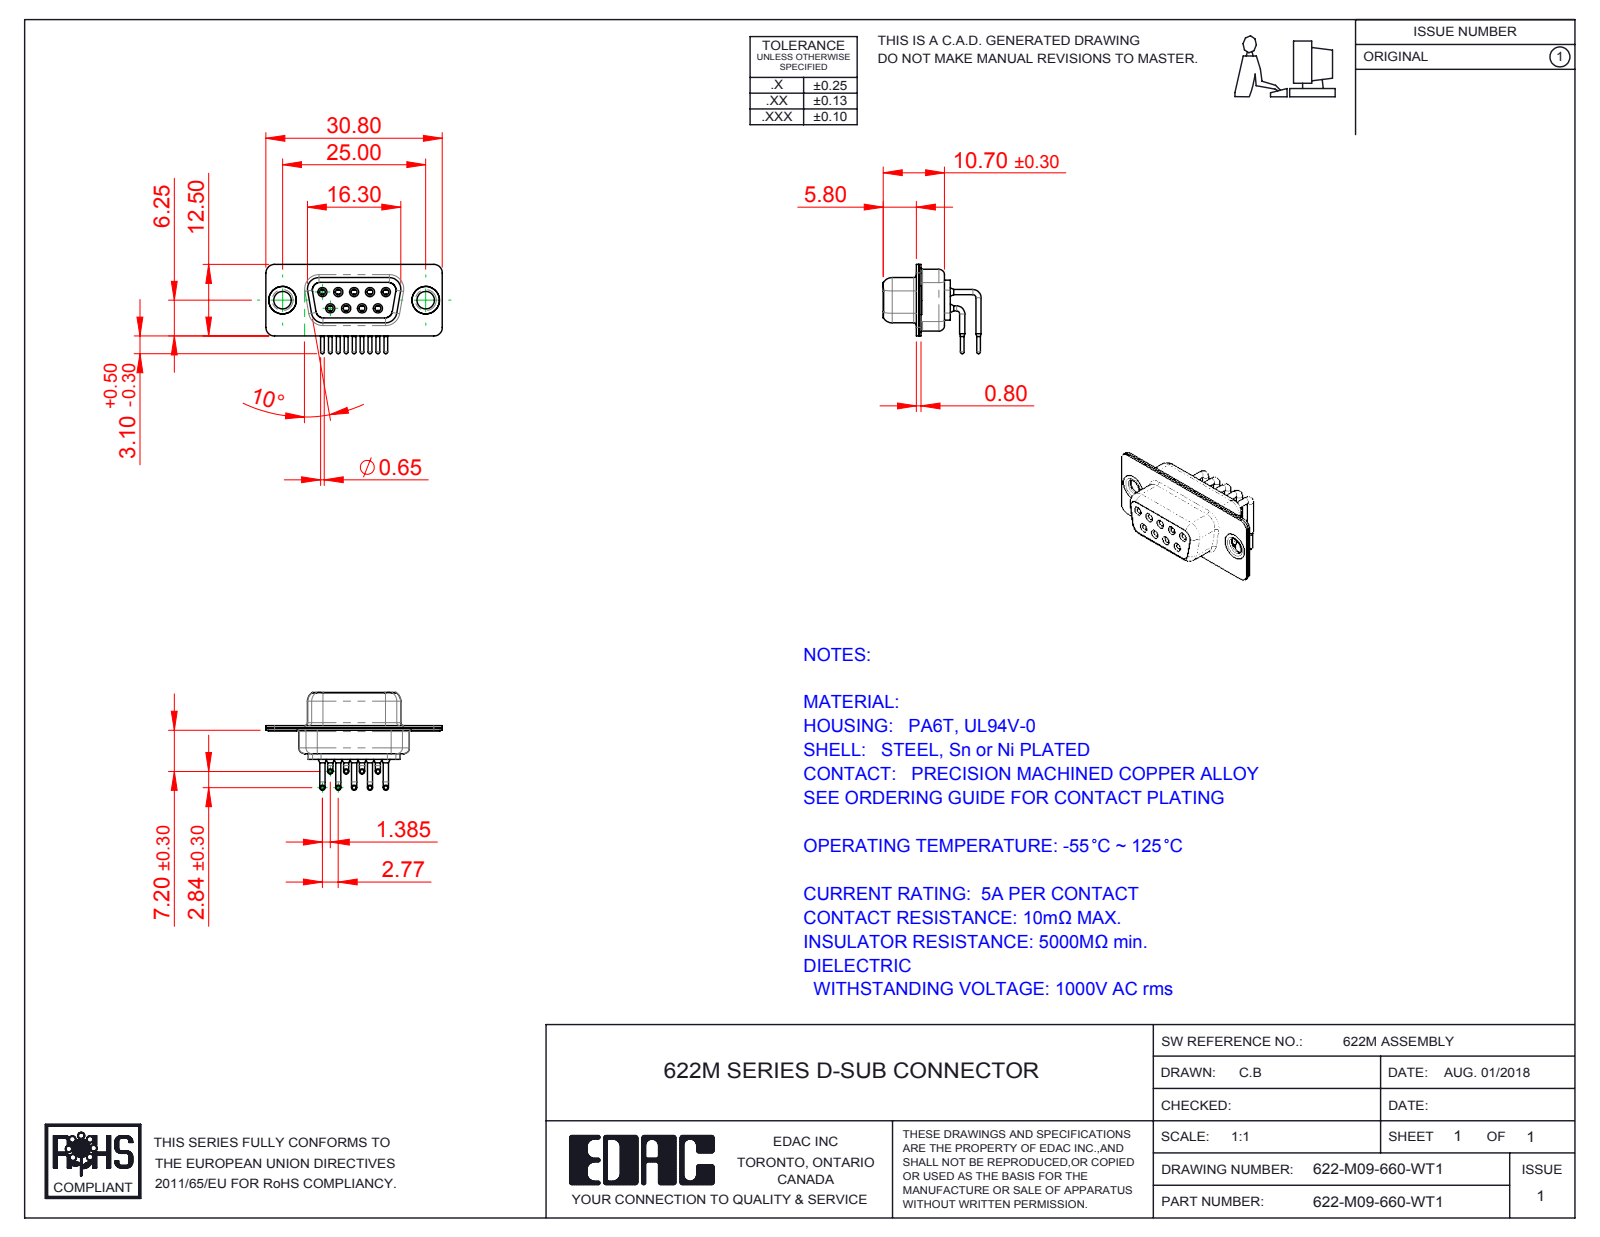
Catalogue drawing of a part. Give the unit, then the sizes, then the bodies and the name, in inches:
Units: inches
Overall size (bounding box): 1.213 × 0.673 × 0.614
Round holes (diameter × count): ⌀0.039 ×9, ⌀0.043 ×9, ⌀0.067 ×9, ⌀0.071 ×9, ⌀0.079 ×9, ⌀0.12 ×2, ⌀0.157 ×2, ⌀0.189 ×2
Round bosses / shafts (diameter × count): ⌀0.035 ×18, ⌀0.063 ×9, ⌀0.059 ×9, ⌀0.026 ×9, ⌀0.197 ×2, ⌀0.193 ×2, ⌀0.14 ×2
Partial cylindrical surfaces — rounded edges, fillets, slot ends (radius × count): R0.059 ×16, R0.079 ×12, R0.053 ×8, R0.063 ×8, R0.01 ×4, R0.02 ×4, R0.024 ×4, R0.026 ×4
Main face-to-face distances: 0.016, 0.031, 0.057, 0.352, 0.091, 0.244, 0.335, 0.075, 0.033, 0.368
Hole centre spacings: 0.124, 0.109, 0.218, 0.198, 0.198, 0.327, 0.28, 0.294
Volume: 0.102 in³ · Surface area: 6.834 in²
Bodies: 14 solids, 730 faces (202 planar, 328 cylindrical, 200 other)
Part name (STEP PRODUCT): 622M Contact Row 1; 622-M09-660-WT1; 622M Contact Row 2; 622M Thru Hole Rivet (+3 more)
STEP written by: SolidWorks 2016 (CONFIG_CONTROL_DESIGN)
